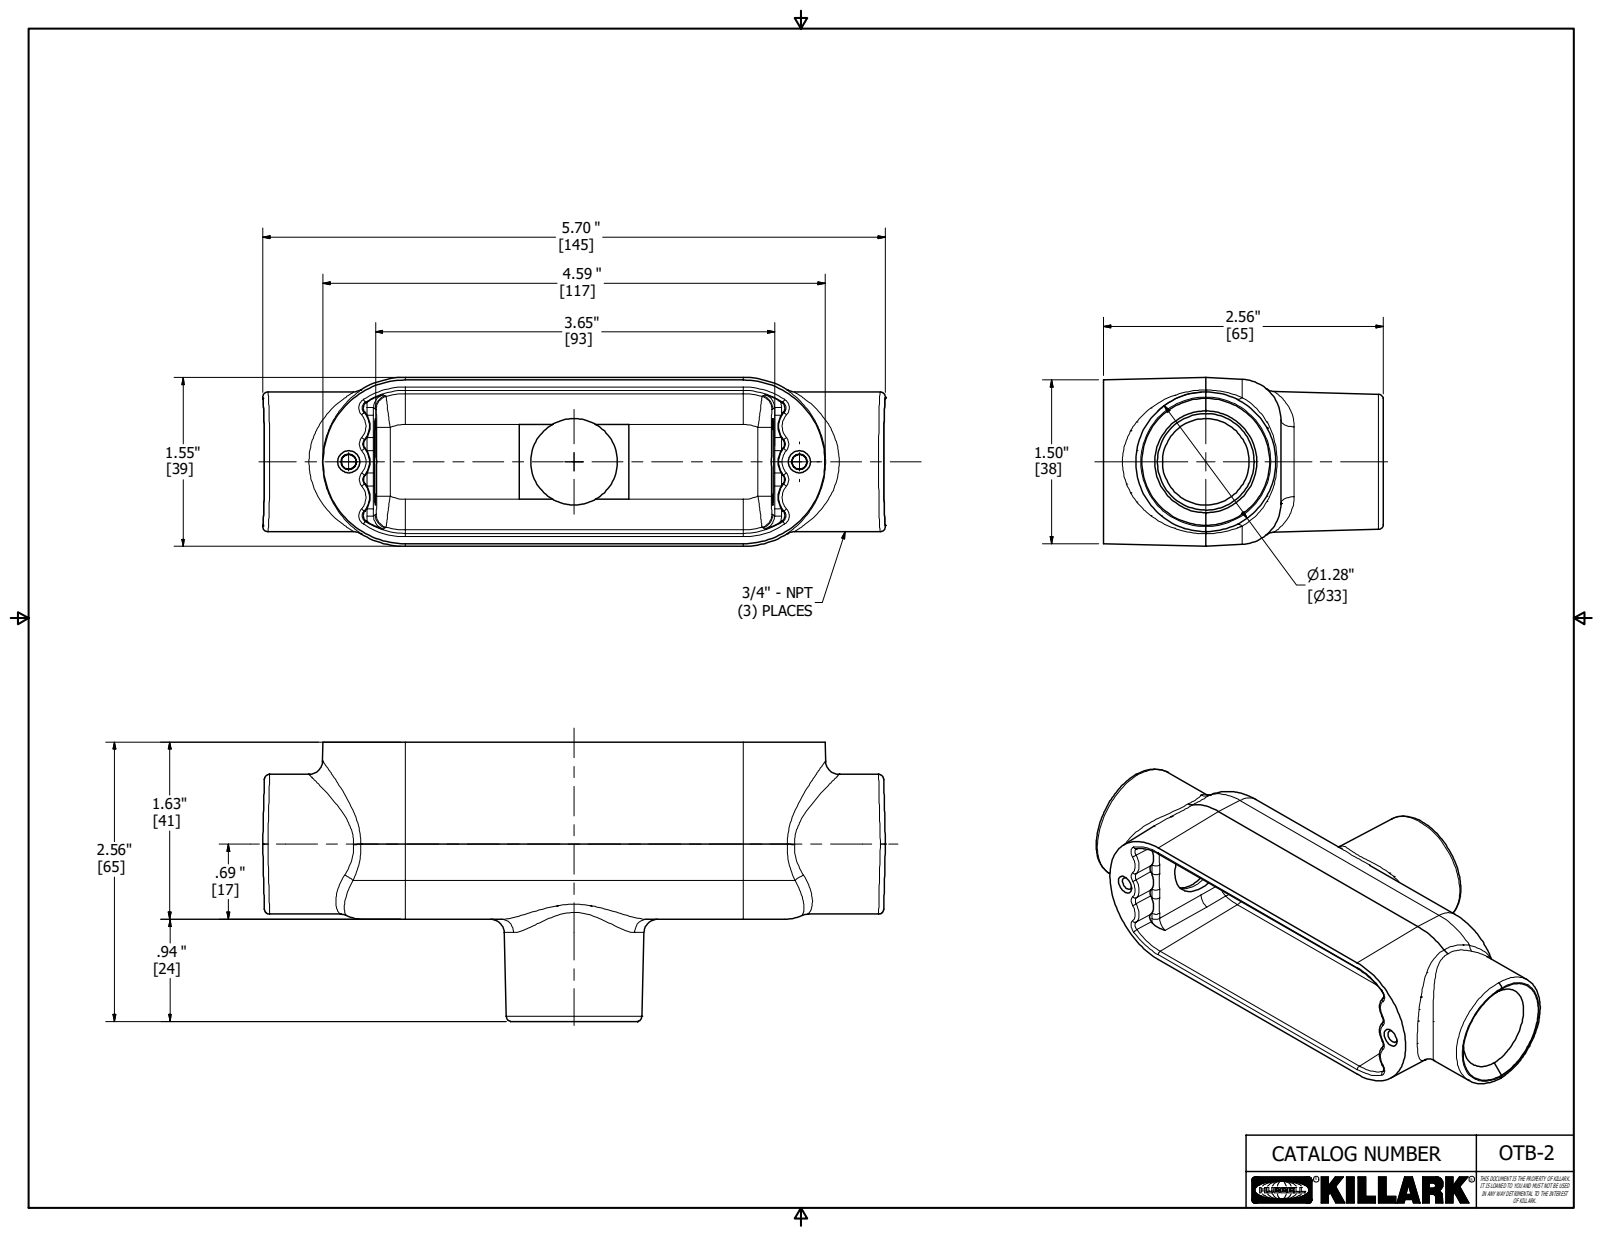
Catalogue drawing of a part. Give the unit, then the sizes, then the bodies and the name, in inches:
Units: inches
Overall size (bounding box): 5.7 × 2.562 × 1.549
Round holes (diameter × count): ⌀0.792 ×2
Round bosses / shafts (diameter × count): ⌀1.281 ×1
Partial cylindrical surfaces — rounded edges, fillets, slot ends (radius × count): R0.031 ×2, R0.062 ×2, R0.125 ×2, R0.281 ×2, R0.375 ×2, R0.644 ×1
Main face-to-face distances: 1.406, 0.124, 1.625, 1.501, 0.122, 1.502, 0.015, 0.107, 0.109, 1.61
Volume: 4.192 in³ · Surface area: 56.89 in²
Bodies: 1 solid, 210 faces (73 planar, 27 cylindrical, 110 other)
Part name (STEP PRODUCT): 13794-1
STEP written by: Autodesk Inventor 2018 (AUTOMOTIVE_DESIGN)
